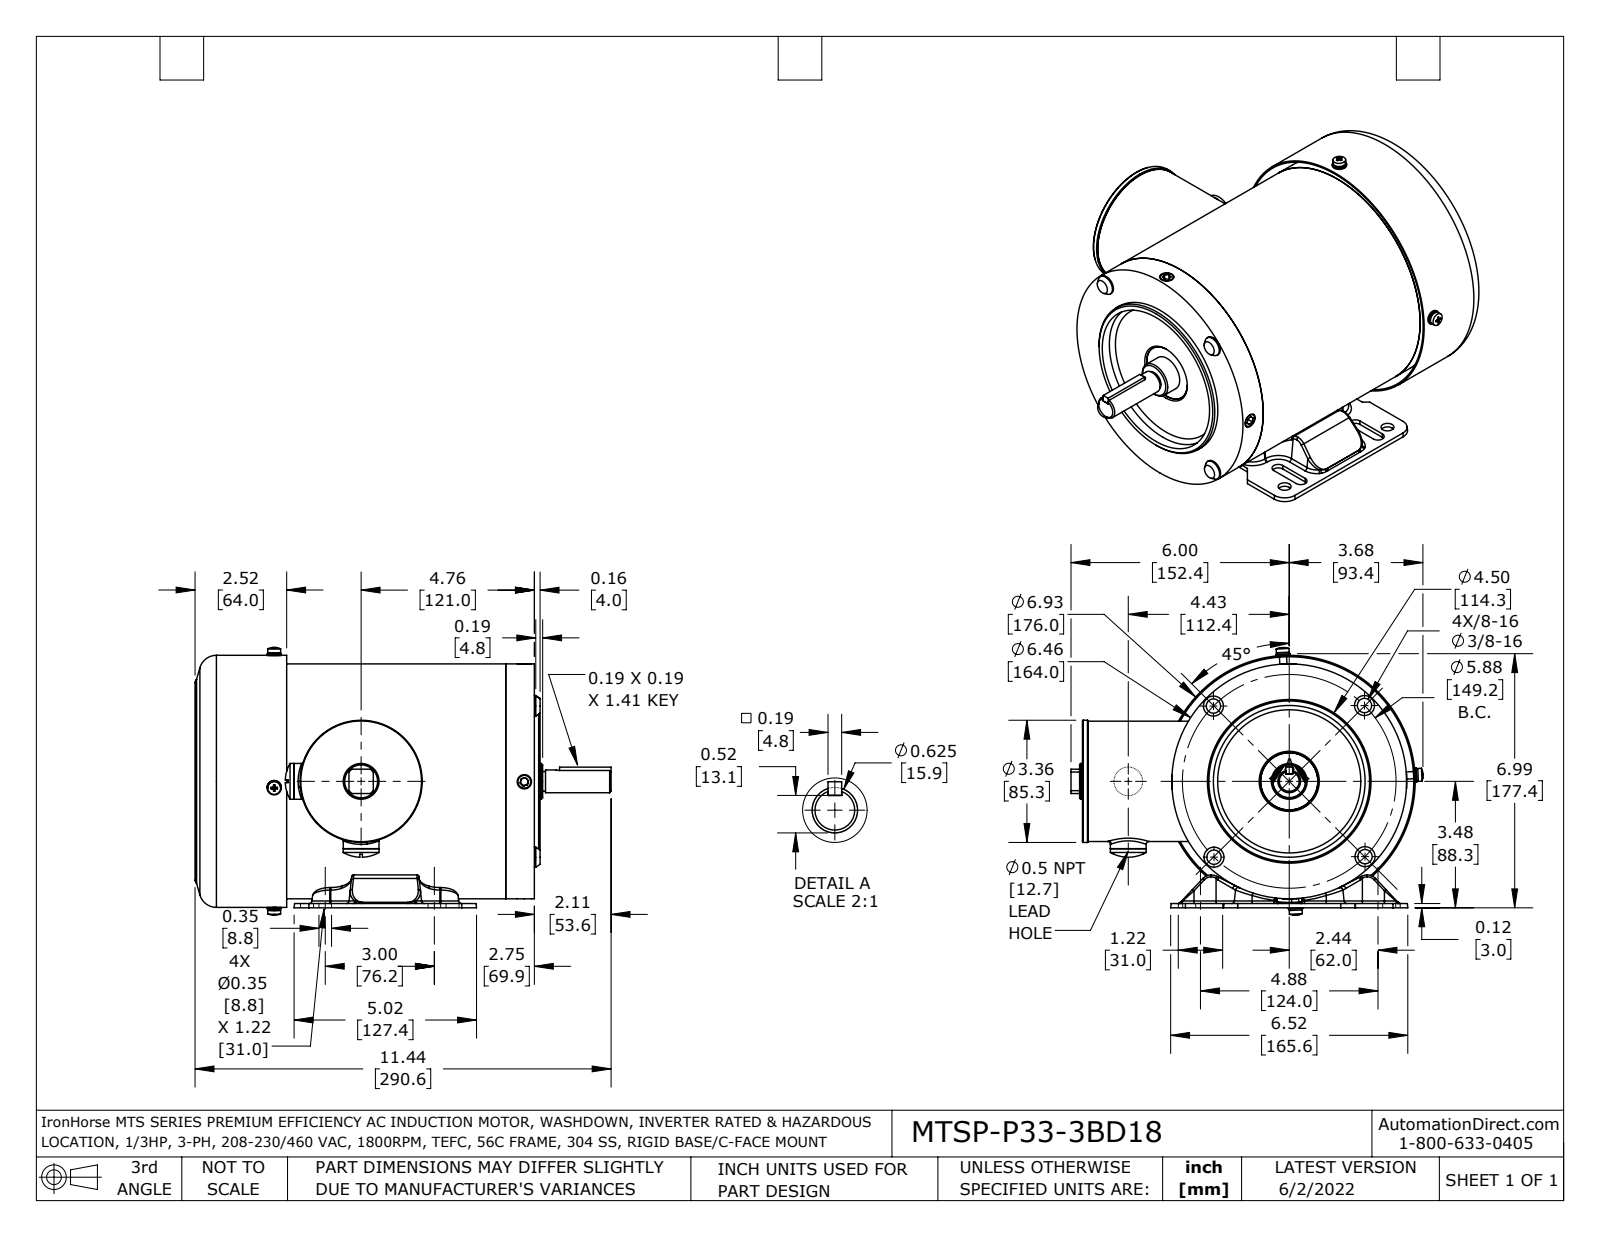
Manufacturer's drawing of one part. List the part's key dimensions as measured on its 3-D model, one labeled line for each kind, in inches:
Part name (STEP PRODUCT): MTSP-P33-3BD18
STEP written by: SolidWorks 2021 (AUTOMOTIVE_DESIGN)
Units: inches
Bodies: 40 solids, 1660 faces (442 planar, 579 cylindrical, 639 other)
Overall size (bounding box): 11.441 × 9.68 × 7.357
Volume: 54.38 in³ · Surface area: 932 in²
Round holes (diameter × count): ⌀0.165 ×10, ⌀0.217 ×8, ⌀0.213 ×4, ⌀0.236 ×4, ⌀0.256 ×4, ⌀0.335 ×4, ⌀0.354 ×4, ⌀0.358 ×4, ⌀0.118 ×2, ⌀0.472 ×2, ⌀0.656 ×2, ⌀1.378 ×2
Round bosses / shafts (diameter × count): ⌀0.394 ×8, ⌀0.551 ×4, ⌀0.354 ×4, ⌀0.331 ×4, ⌀0.315 ×4, ⌀0.197 ×4, ⌀0.984 ×3, ⌀0.787 ×2
Partial cylindrical surfaces — rounded edges, fillets, slot ends (radius × count): R0.079 ×58, R0.039 ×39, R0.128 ×36, R0.012 ×16, R0.118 ×14, R0.173 ×8, R0.236 ×8, R0.059 ×6
Main face-to-face distances: 0.118, 7.323, 0.236, 0.039, 7.087, 7.205, 7.441, 1.949, 1.831, 9.272
Hole centre spacings: 2.937, 4.154, 0.133, 1.181, 1.312, 1.917, 2.992, 3.163
